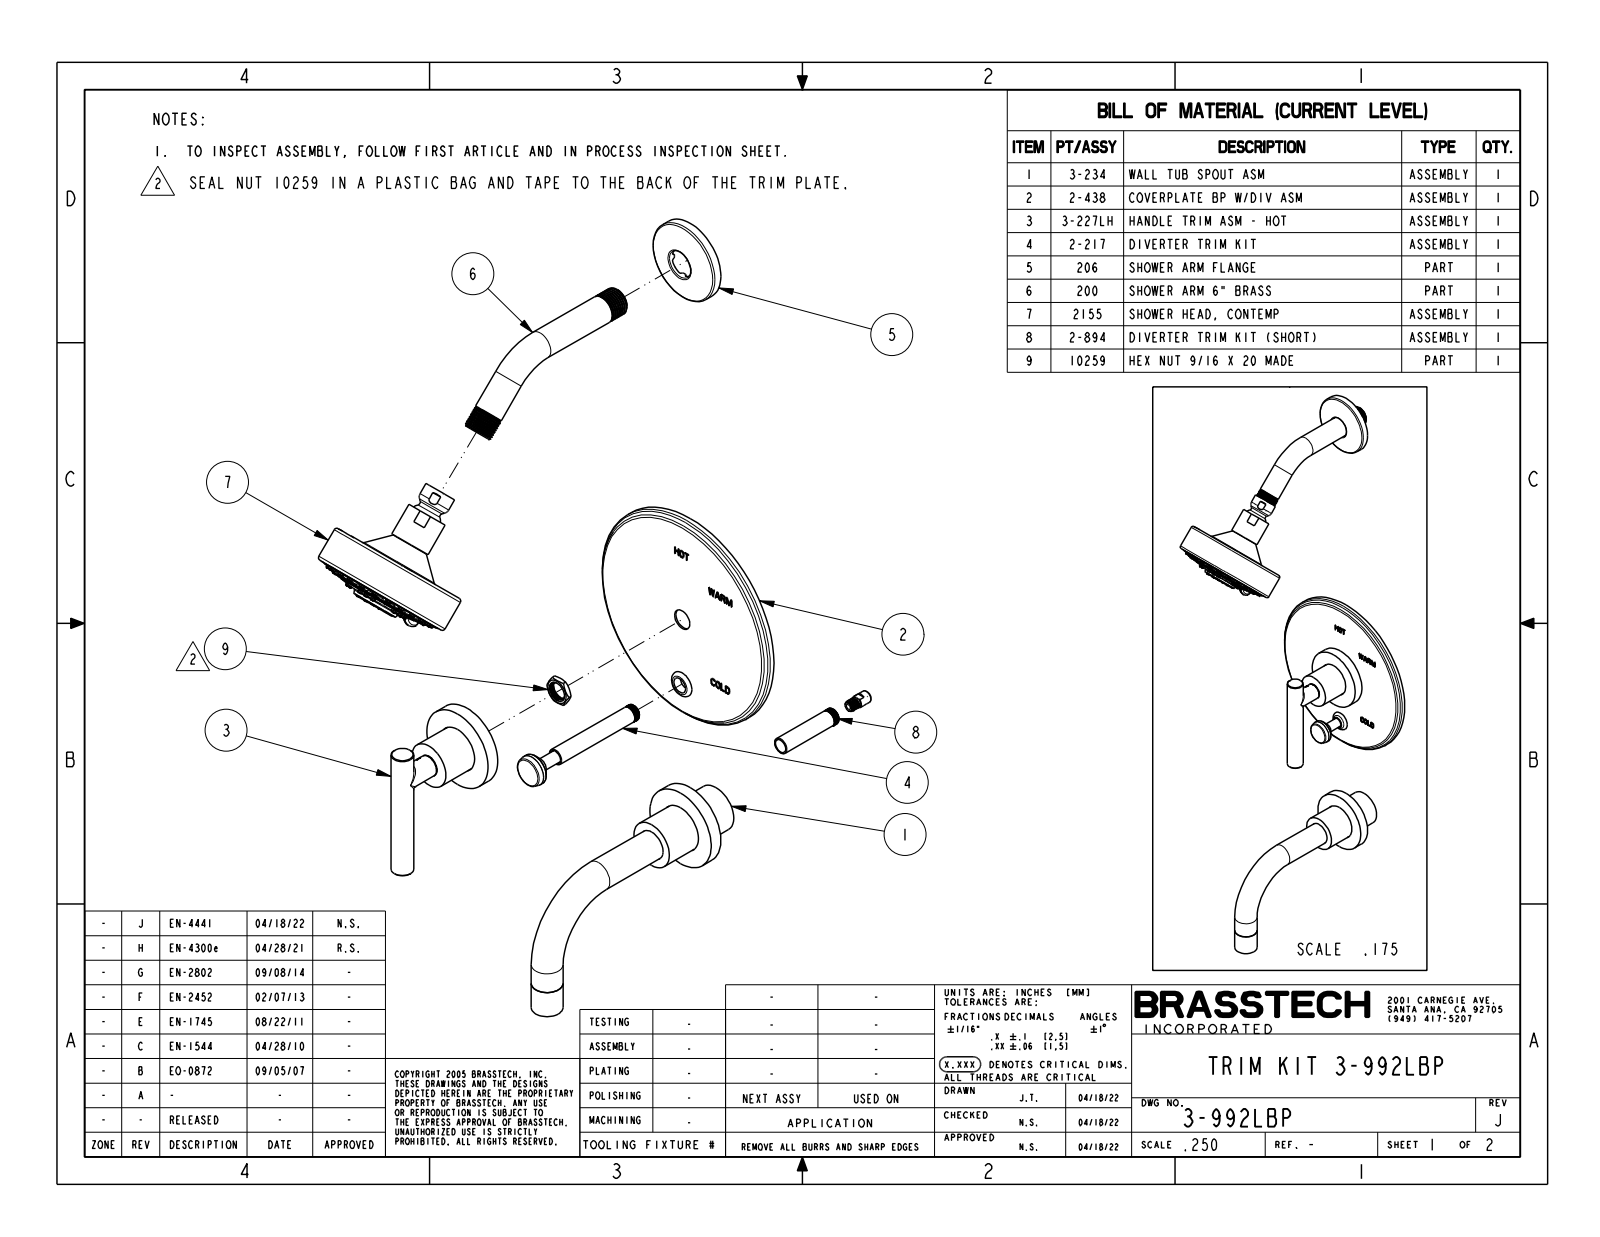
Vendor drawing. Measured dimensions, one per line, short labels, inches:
name: 3-992LBP
written by: CREO PARAMETRIC BY PTC INC, 2018400 (CONFIG_CONTROL_DESIGN)
unit: in
bodies: 3 solids, 1370 faces (404 planar, 217 cylindrical, 749 other)
size: 23.63 × 8.175 × 6.5
volume: 44.41 in³; area: 203.4 in²
holes: 8× ⌀0.059, 1× ⌀0.925
bosses: 39× ⌀0.142, 23× ⌀0.165, 2× ⌀2.375, 2× ⌀0.875, 2× ⌀0.813, 2× ⌀0.625, 1× ⌀6.5, 1× ⌀4
rounds: 8× R0.079, 2× R0.02, 1× R0.138, 1× R0.472, 1× R0.512, 1× R0.63
face distances: 0.313, 0.062, 0.688, 0.375, 0.375, 0.313, 1.796, 1.483, 1.421, 1.108
hole spacings: 0.443, 0.579, 0.818, 0.819, 1.069, 0.443, 0.578, 1.069
